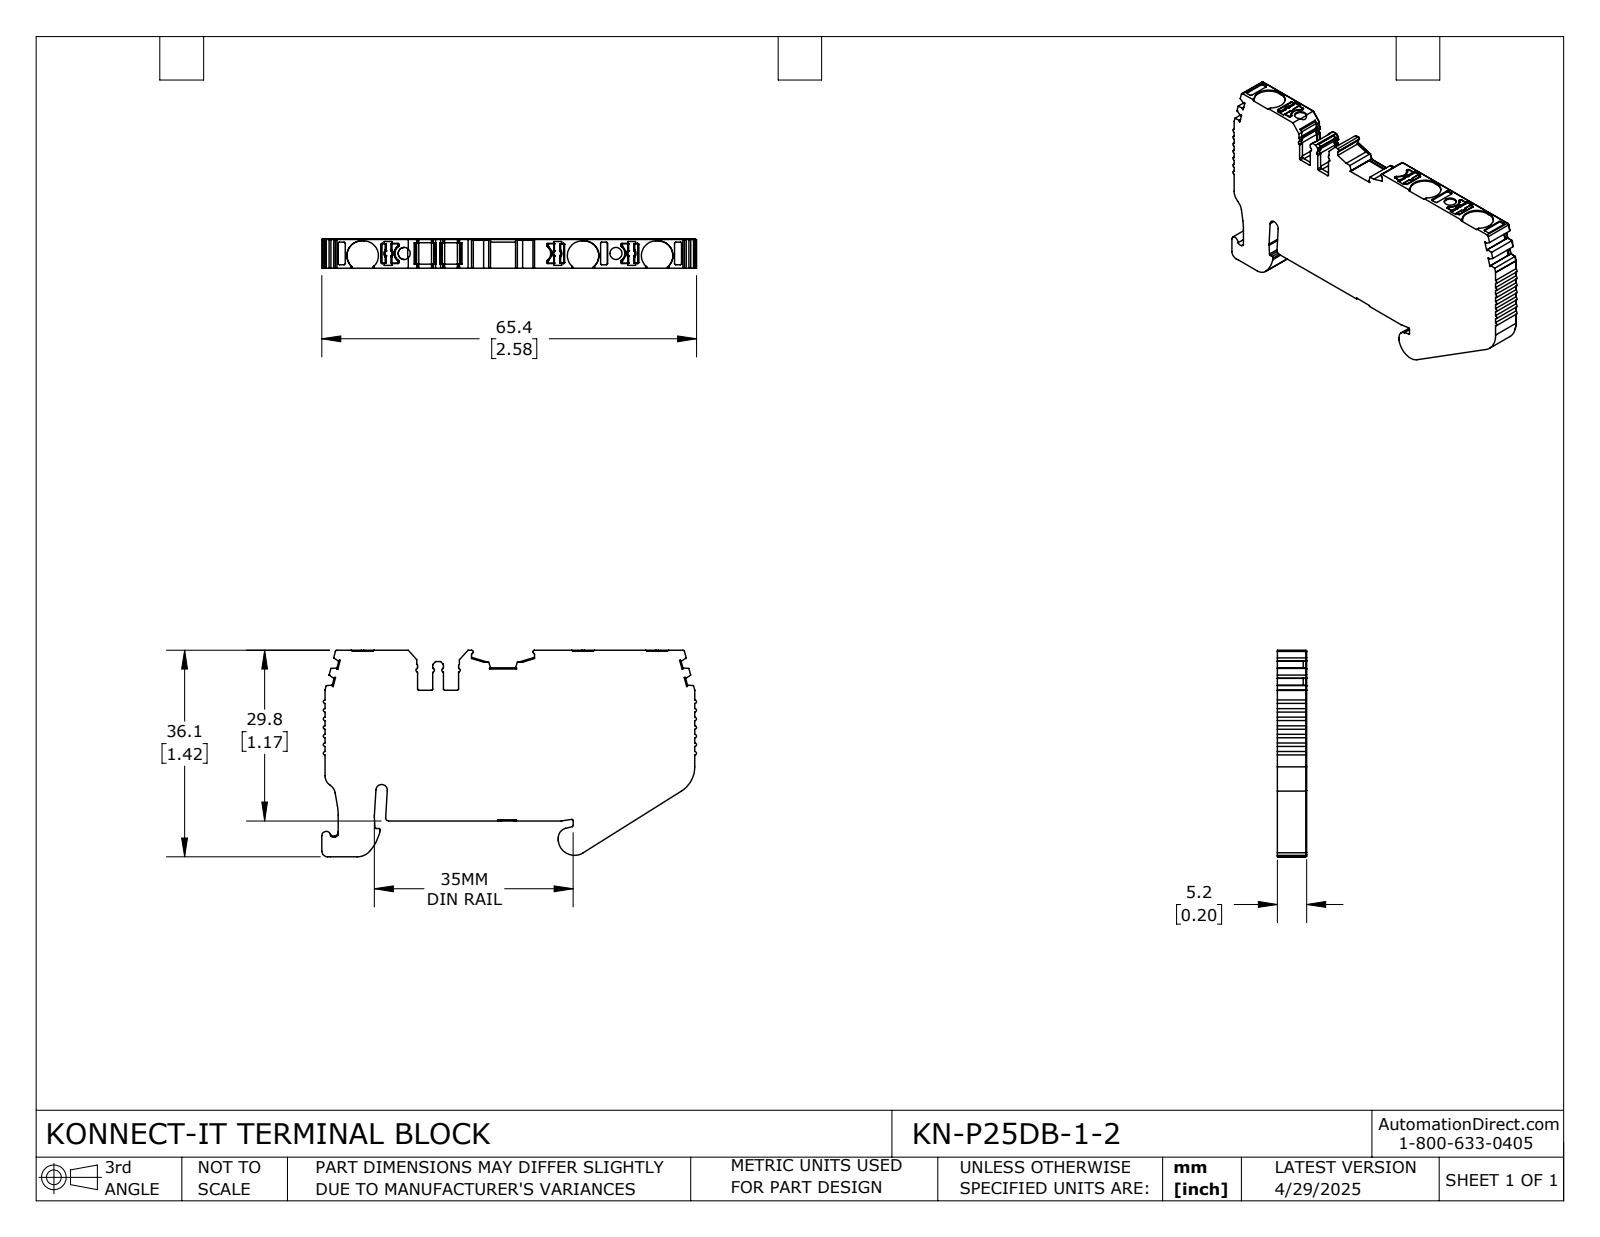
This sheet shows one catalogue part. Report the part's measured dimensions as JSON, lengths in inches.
{"part_name": "KN-P25DB-1-2", "step_written_by": "SolidWorks 2024 (CONFIG_CONTROL_DESIGN)", "units": "inches", "bodies": {"solids": 1, "faces": 655, "planar": 345, "cylindrical": 259, "other": 51}, "overall_size": [2.576, 1.42, 0.203], "volume_in3": 0.584, "surface_area_in2": 7.967, "round_holes": [[0.083, 2]], "partial_cylinders_radius": [[0.008, 66], [0.012, 39], [0.004, 19], [0.02, 18], [0.006, 12], [0.016, 9], [0.1, 6], [0.039, 3]], "face_to_face_distances": [0.203, 1.166, 1.174, 2.543, 0.177, 0.197, 0.246, 1.412, 0.079, 1.42], "hole_center_spacings": [1.456]}
